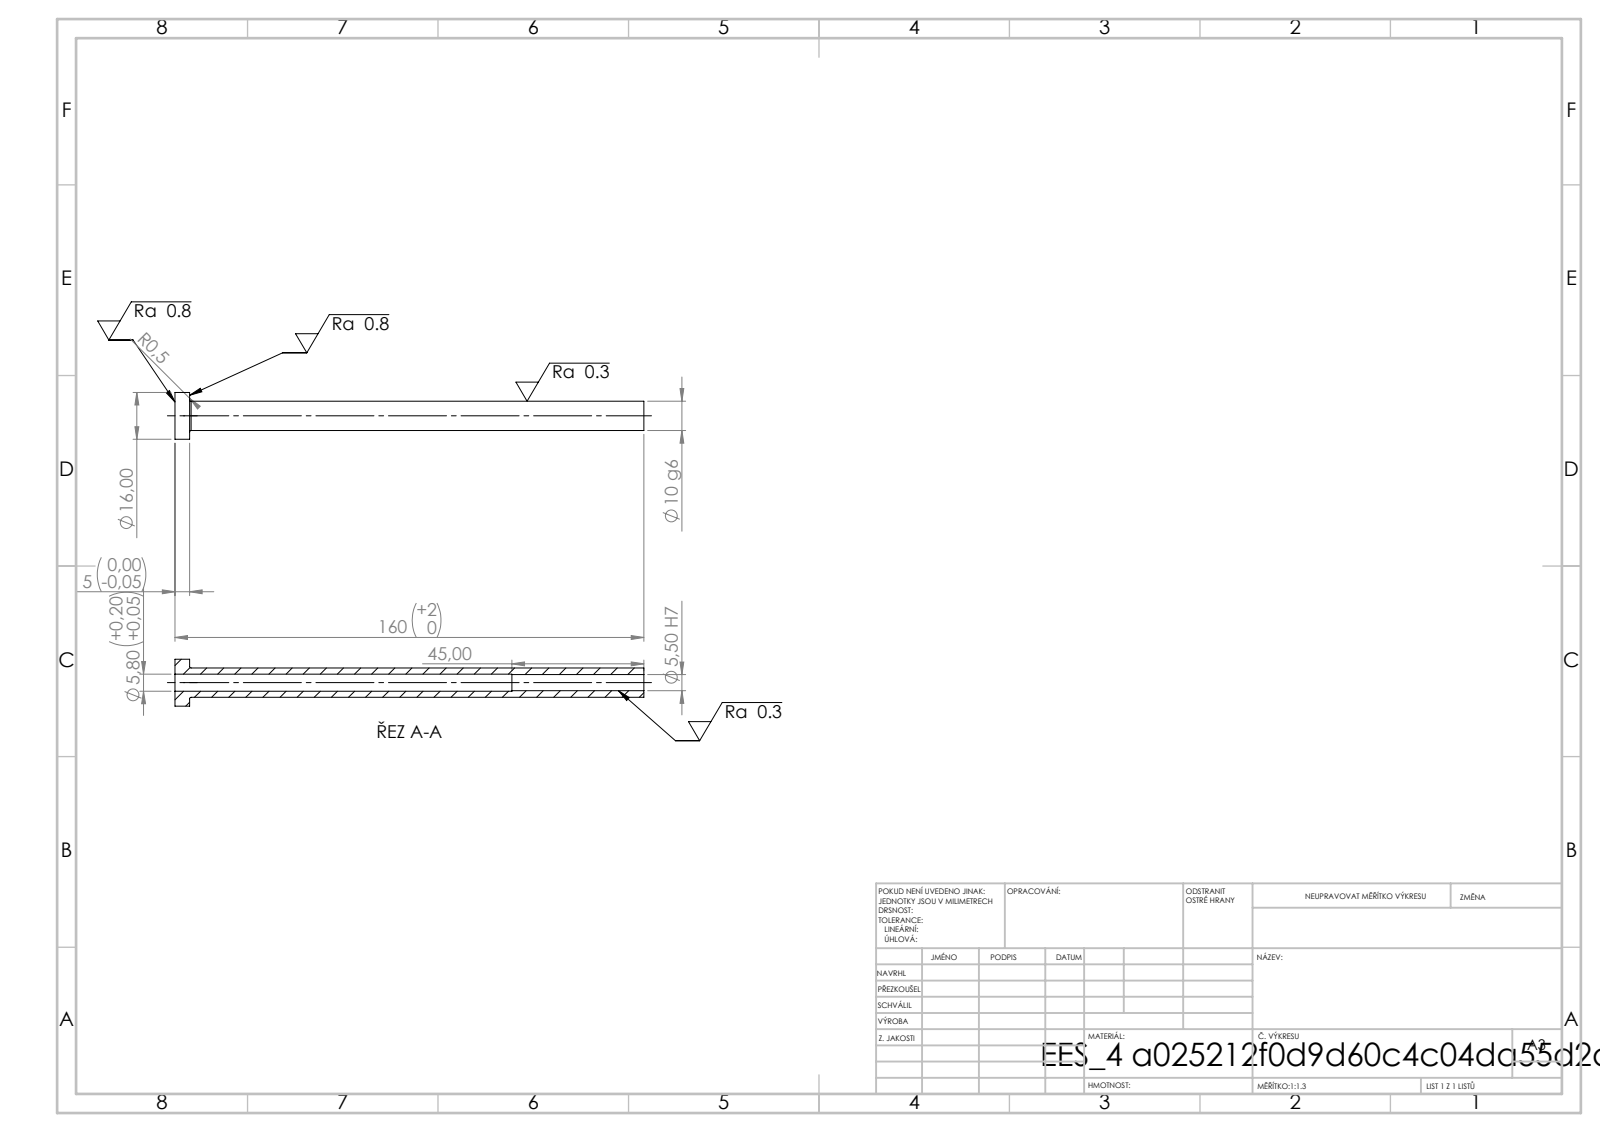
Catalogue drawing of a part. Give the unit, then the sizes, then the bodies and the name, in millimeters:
Units: millimetres
Overall size (bounding box): 160 × 16 × 16
Round holes (diameter × count): ⌀5.5 ×1, ⌀5.8 ×1
Round bosses / shafts (diameter × count): ⌀16 ×1, ⌀10 ×1
Main face-to-face distances: 5, 160, 155, 115, 110, 45
Volume: 9 073 mm³ · Surface area: 8 342 mm²
Bodies: 1 solid, 14 faces (4 planar, 8 cylindrical, 2 other)
STEP written by: SolidWorks 2019 (CONFIG_CONTROL_DESIGN)
